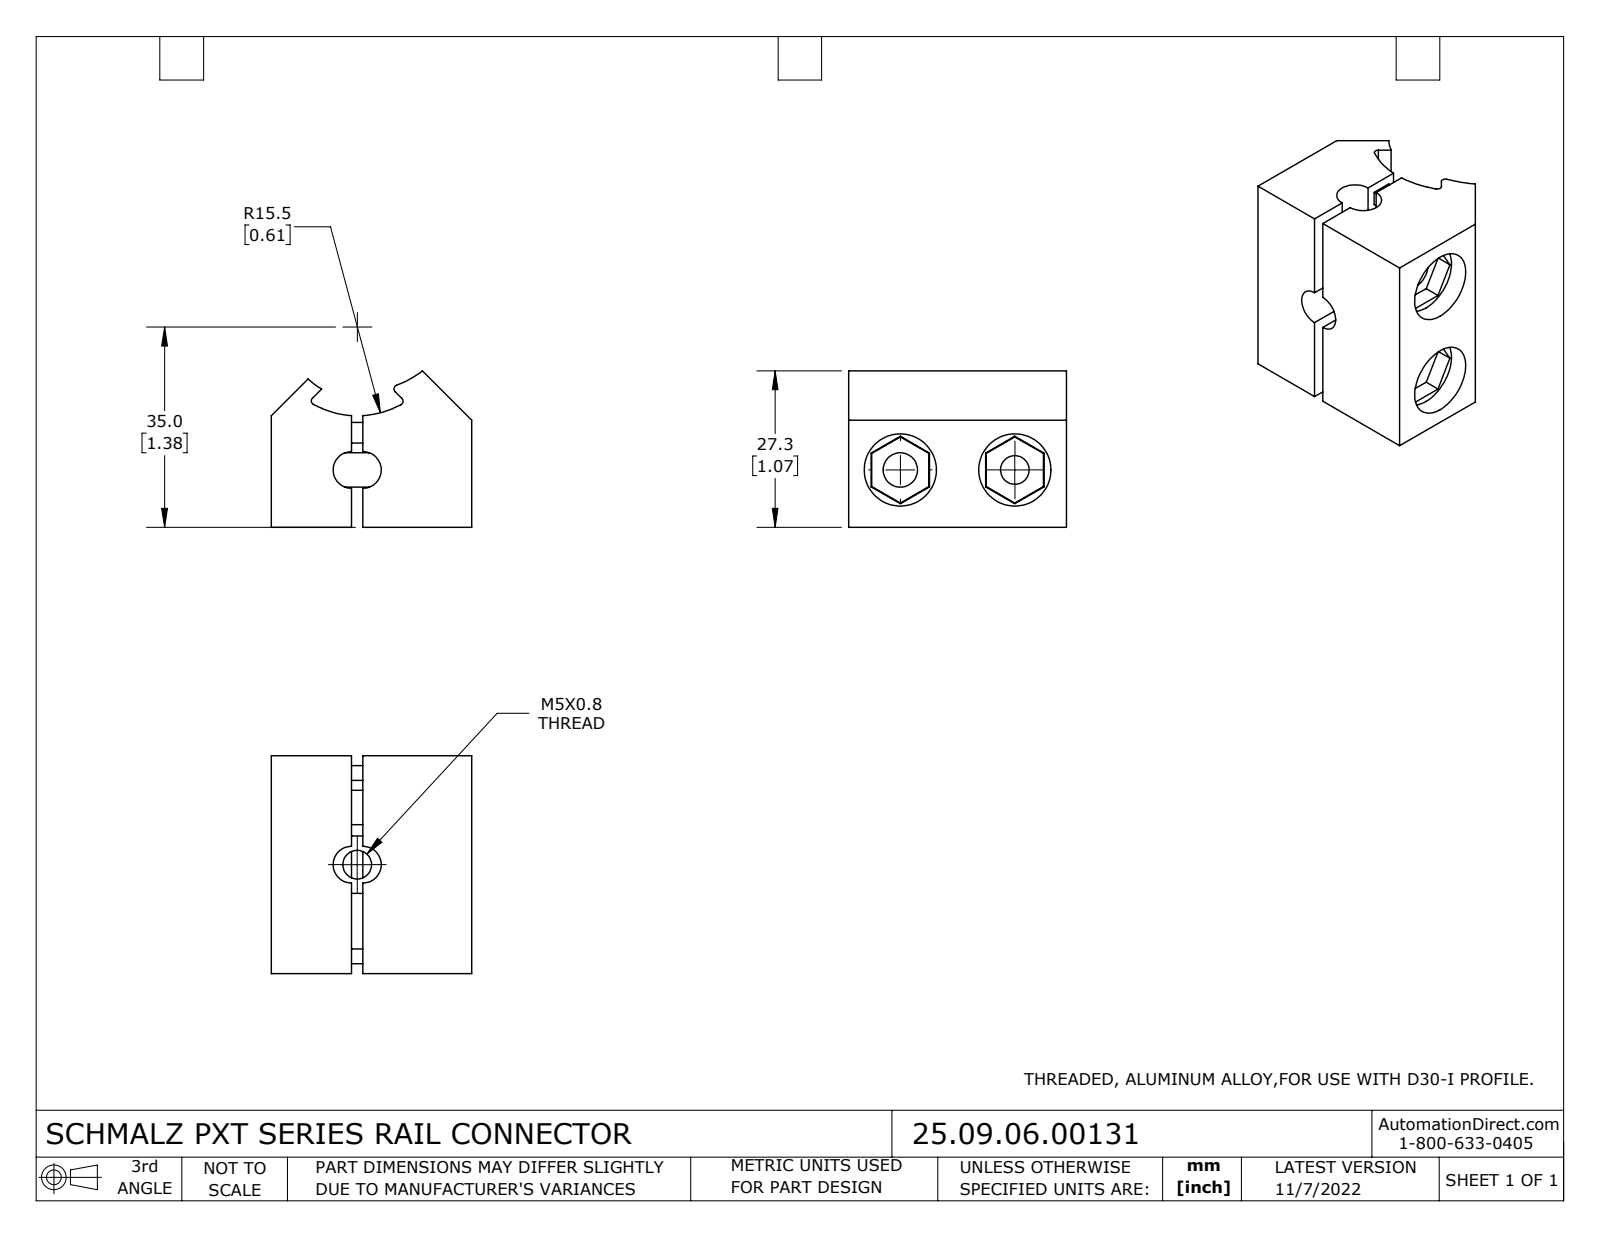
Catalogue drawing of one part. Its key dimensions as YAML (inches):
part_name: "25.09.06.00131"
step_written_by: "SolidWorks 2021 (CONFIG_CONTROL_DESIGN)"
units: inches
bodies: {solids: 5, faces: 150, planar: 95, cylindrical: 55, other: 0}
overall_size: [1.496, 1.378, 1.075]
volume: 1.466
surface_area: 17.75
round_holes:
  - {diameter: 0.197, count: 3}
  - {diameter: 0.256, count: 2}
  - {diameter: 0.496, count: 2}
round_bosses_or_shafts:
  - {diameter: 0.394, count: 1}
  - {diameter: 0.236, count: 1}
partial_cylinders:
  - {radius: 0.126, count: 4}
  - {radius: 0.028, count: 3}
  - {radius: 1.266, count: 2}
  - {radius: 0.492, count: 1}
  - {radius: 0.61, count: 1}
  - {radius: 0.677, count: 1}
face_to_face_distances: [1.496, 0.398, 0.394, 0.551, 0.748, 0.402, 1.378, 0.827, 0.079, 0.63]
hole_center_spacings: [0.787]
